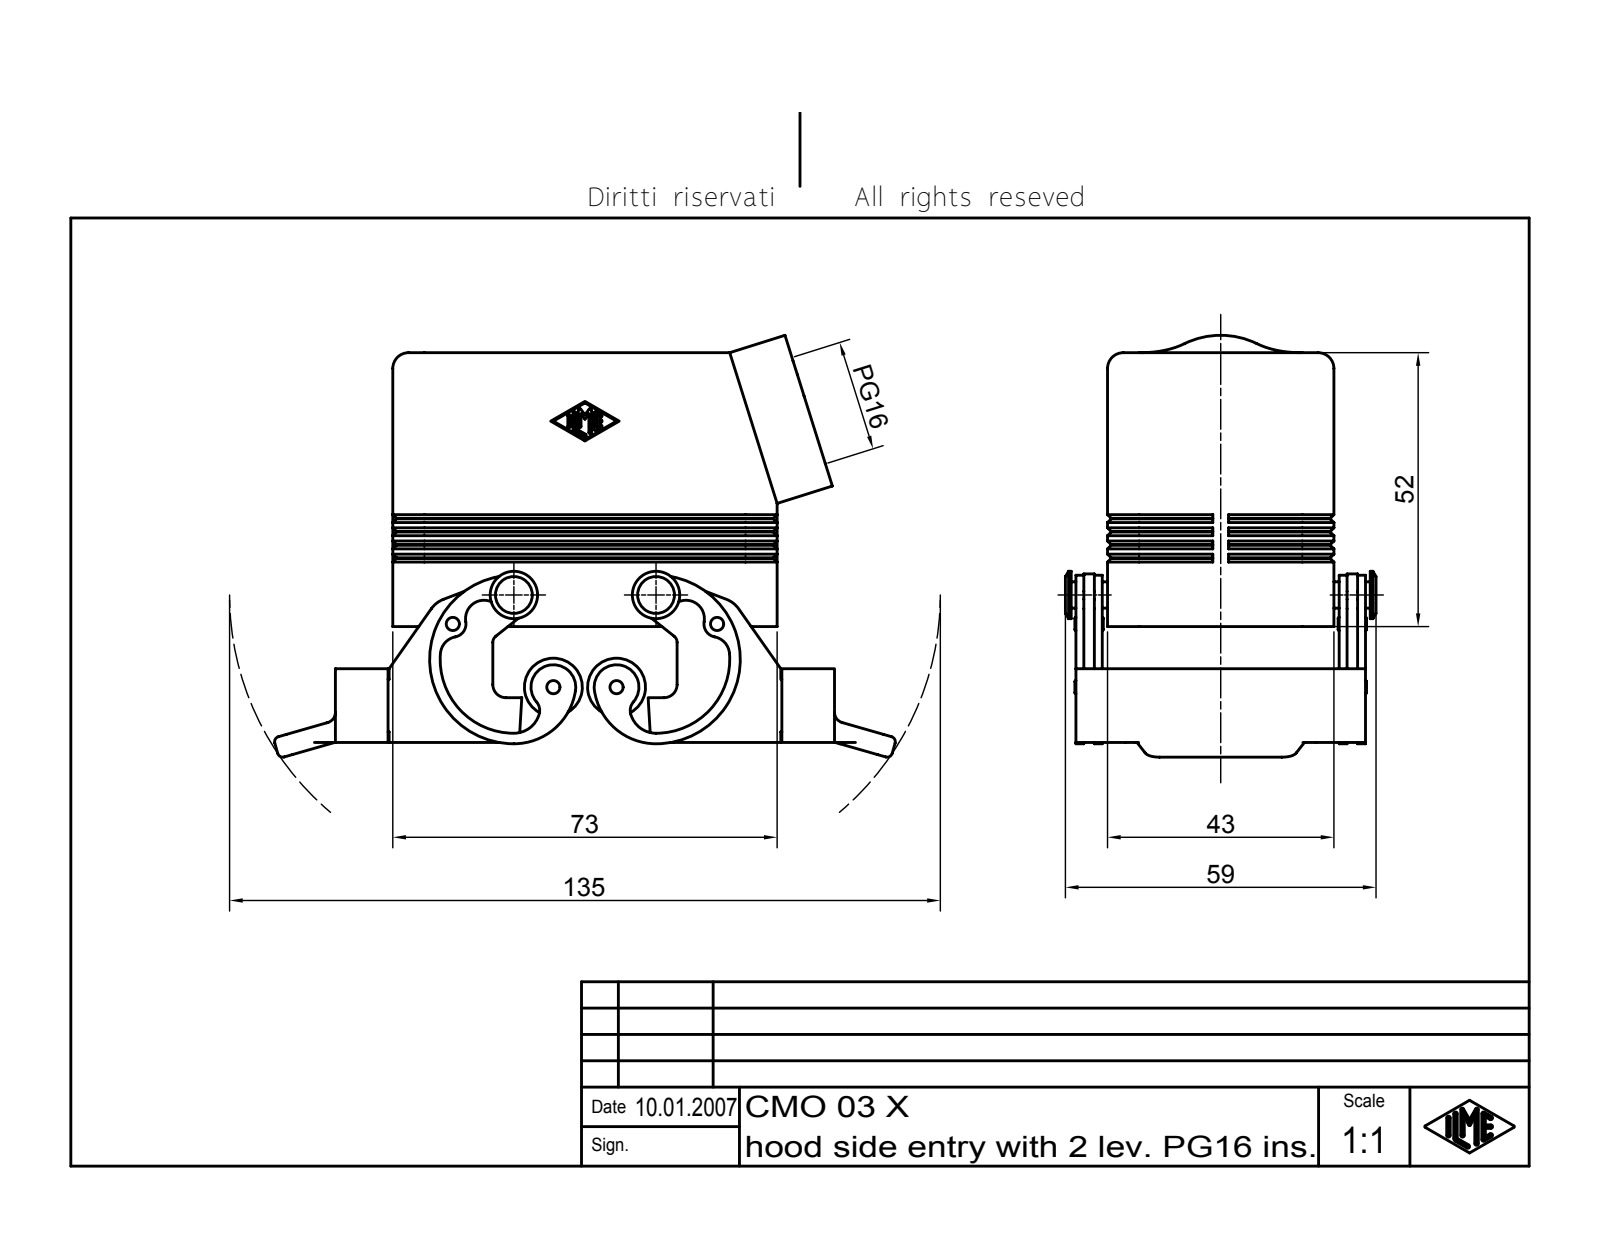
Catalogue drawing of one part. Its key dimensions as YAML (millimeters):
part_name: "CHO Tüllengehäuse 2 Bügel für einen Einsatz"
step_written_by: "Autodesk Inventor 7 (AUTOMOTIVE_DESIGN)"
units: millimeters
bodies: {solids: 1, faces: 818, planar: 236, cylindrical: 209, other: 373}
overall_size: [117.9, 80.09, 59]
volume: 74298
surface_area: 45276
round_holes:
  - {diameter: 2.5, count: 2}
  - {diameter: 19.16, count: 1}
  - {diameter: 21.16, count: 1}
round_bosses_or_shafts:
  - {diameter: 11, count: 2}
  - {diameter: 9, count: 2}
  - {diameter: 5, count: 2}
  - {diameter: 2, count: 2}
partial_cylinders:
  - {radius: 0.25, count: 14}
  - {radius: 1, count: 12}
  - {radius: 3, count: 11}
  - {radius: 2, count: 10}
  - {radius: 2.5, count: 6}
  - {radius: 3.5, count: 4}
  - {radius: 5, count: 4}
  - {radius: 6, count: 4}
face_to_face_distances: [3, 40, 43, 37, 11.5, 8.5, 50, 49, 4, 3.5]
hole_center_spacings: [50.2]
